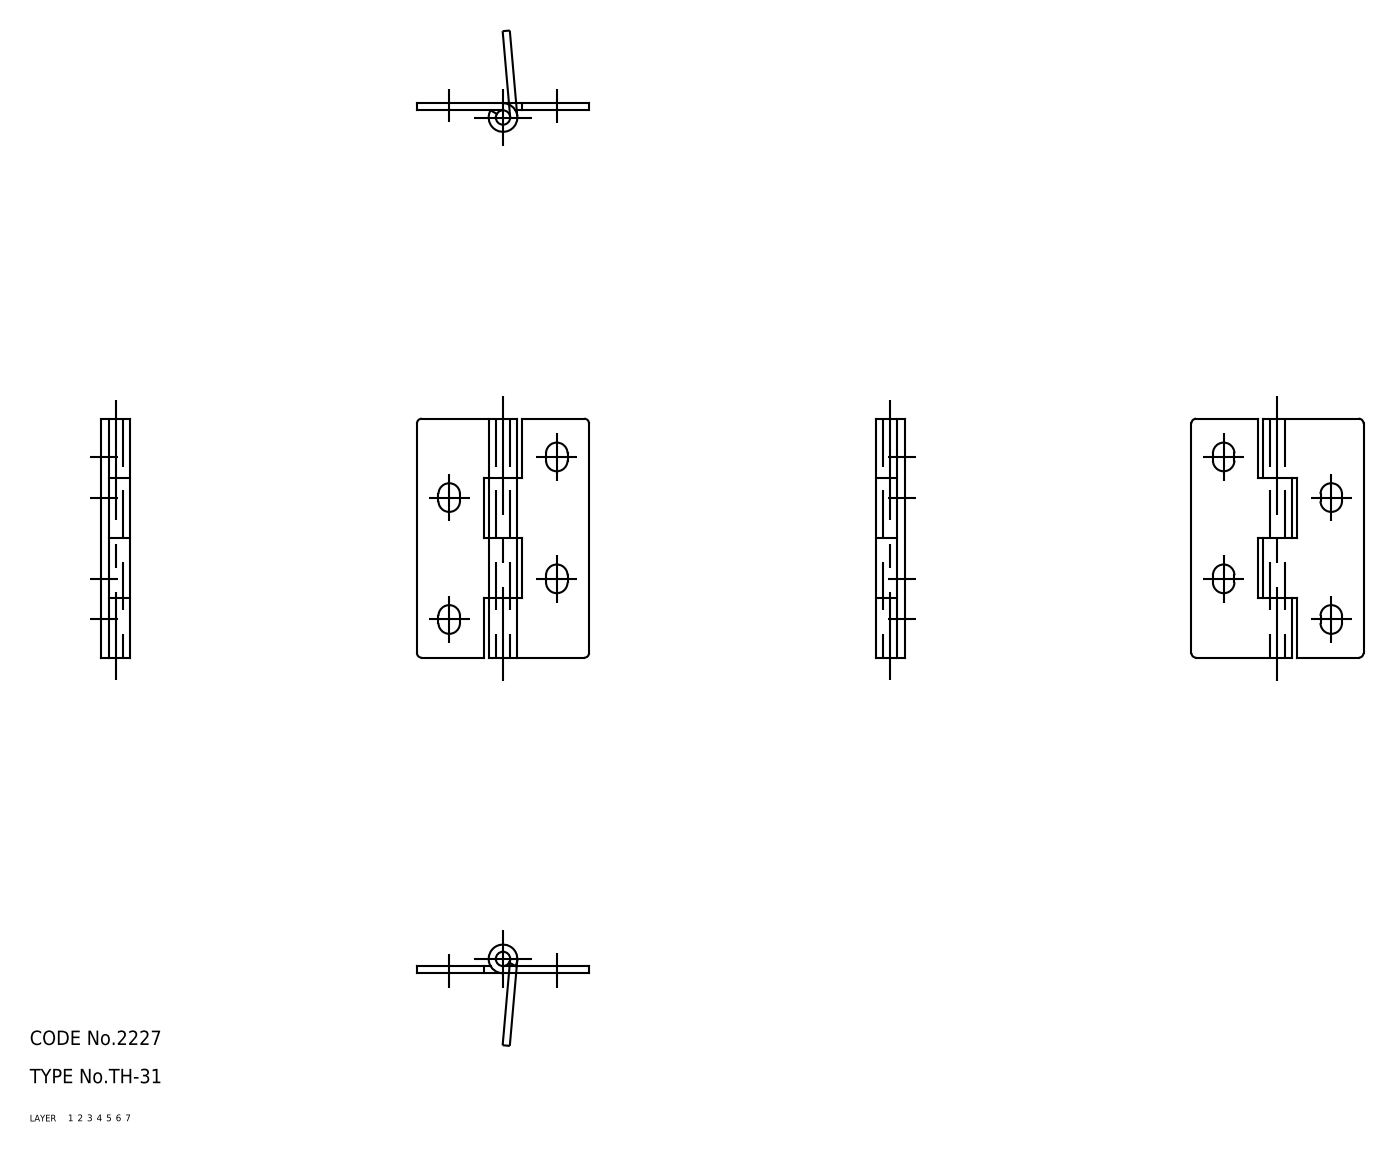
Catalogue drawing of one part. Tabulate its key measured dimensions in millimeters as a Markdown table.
| quantity | value |
| --- | --- |
| part name | hinge piece_B; hinge piece_A; shaft; TH_31_7694_36 |
| STEP written by | CADfix (AUTOMOTIVE_DESIGN) |
| units | millimeters |
| bodies | 3 solids, 56 faces (0 planar, 0 cylindrical, 56 other) |
| overall size | 50 × 36 × 6 |
| volume | 3 497 mm³ |
| surface area | 5 350 mm² |
